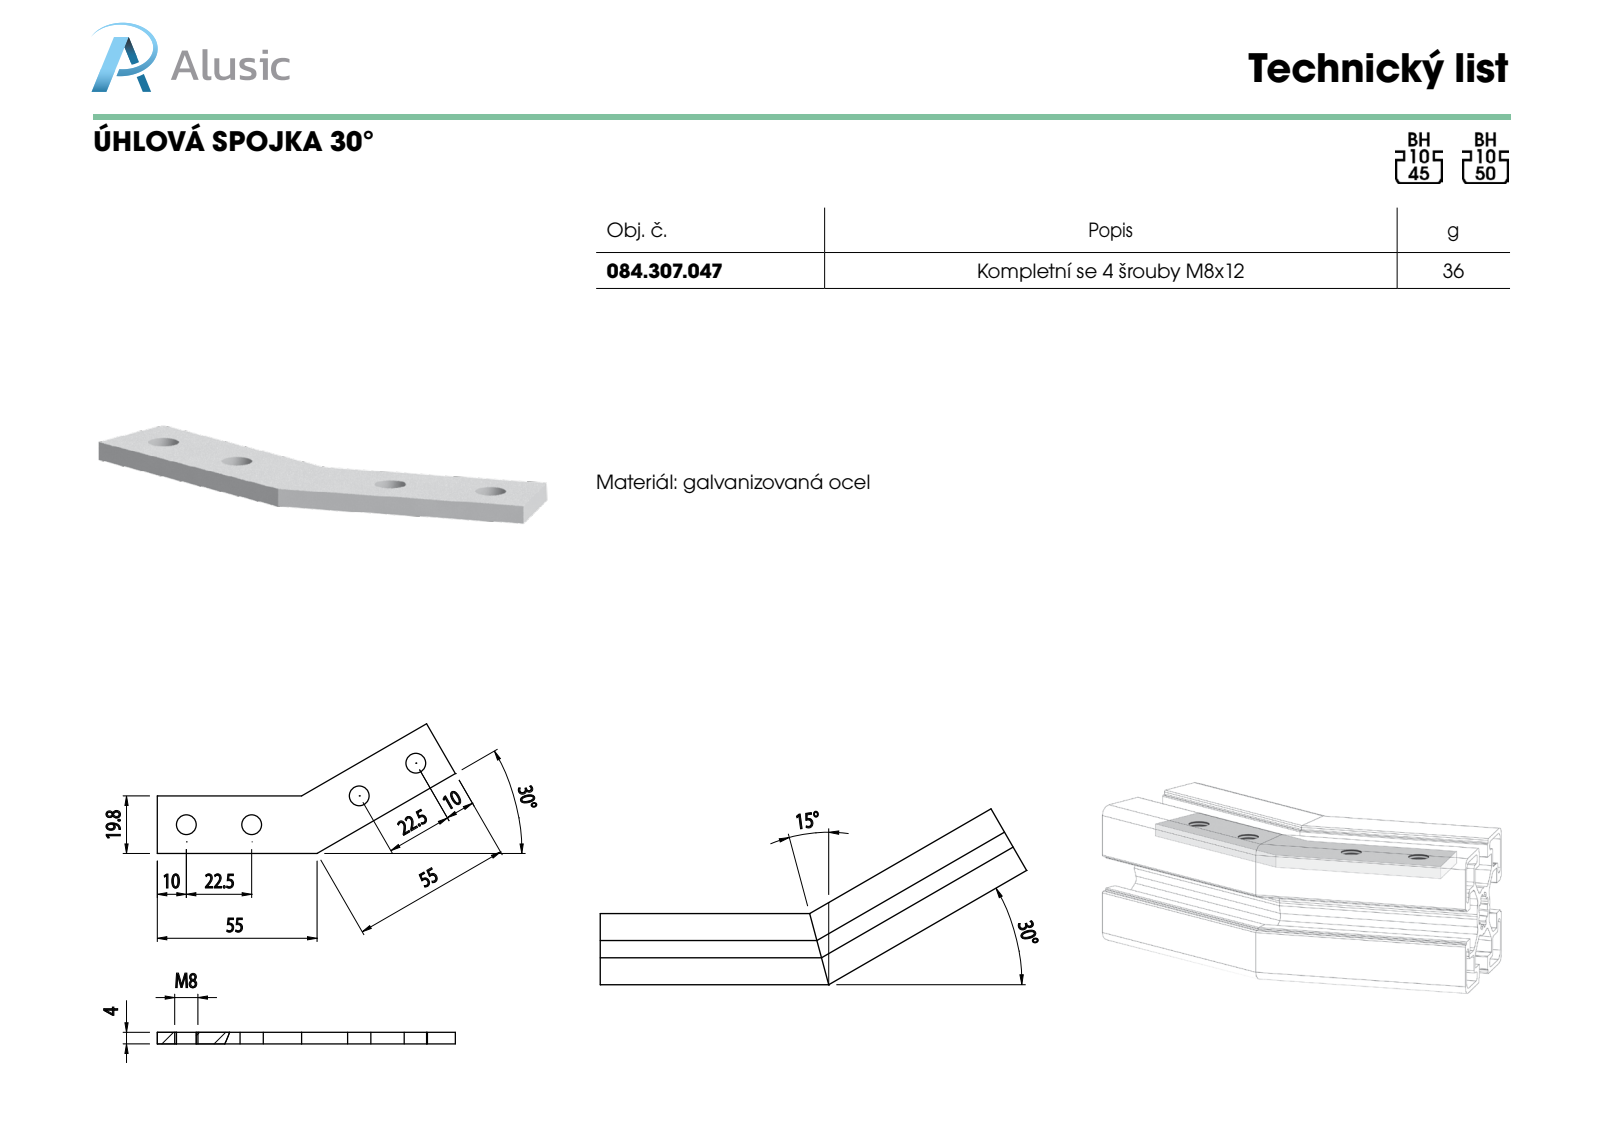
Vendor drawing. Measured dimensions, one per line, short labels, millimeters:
name: 084.307.047
written by: SolidWorks 2012 (CONFIG_CONTROL_DESIGN)
unit: mm
bodies: 1 solid, 16 faces (8 planar, 8 cylindrical, 0 other)
size: 102.63 × 44.65 × 4
volume: 7 711 mm³; area: 5 193 mm²
holes: 4× ⌀6.8
face distances: 4, 19.8
hole spacings: 22.5, 60.35, 38.34, 81.81
